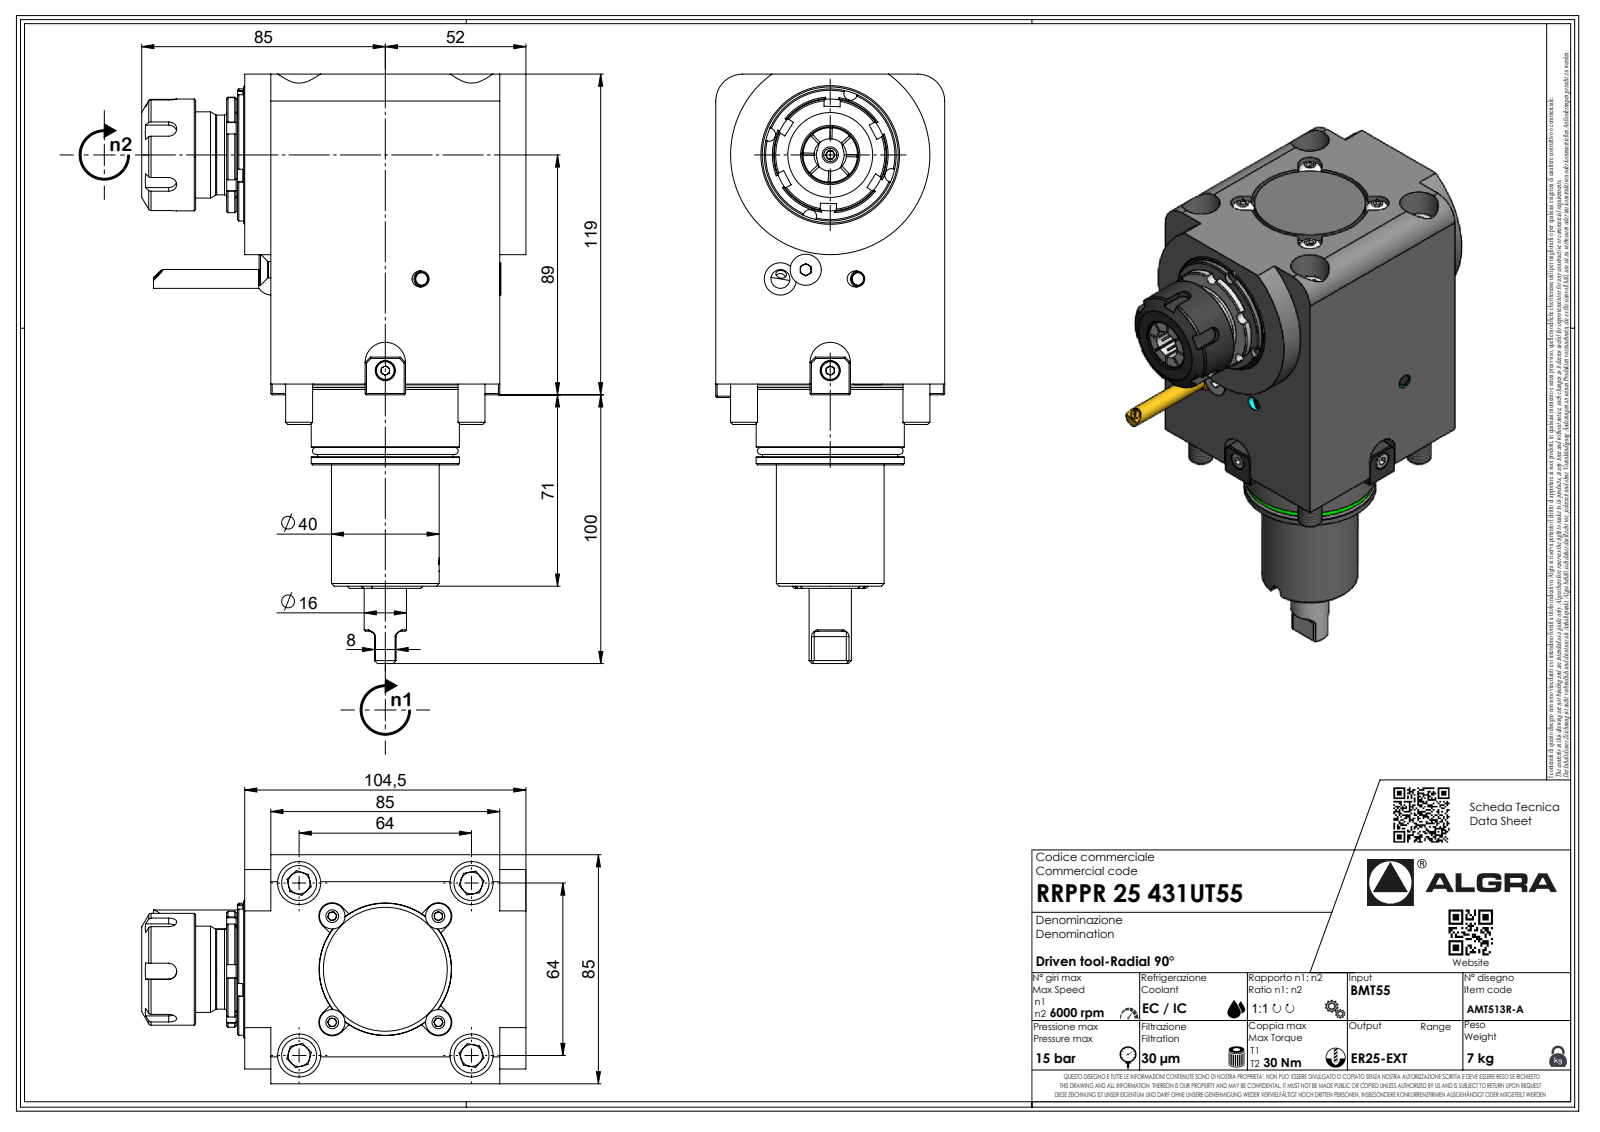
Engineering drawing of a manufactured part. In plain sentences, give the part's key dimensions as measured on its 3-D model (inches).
The part is named "RRPPR25431UT55". Its 3-D file was written by "SolidWorks 2016 (AUTOMOTIVE_DESIGN)". It is 1 solid with 591 faces: 376 planar, 78 cylindrical and 137 other. Overall it measures 8.61 by 5.444 by 3.346 inches. Its volume is 66.21 cubic inches and its surface area 125.1 square inches. Round holes: 1 of diameter 0.124, 1 of diameter 0.157. Round bosses or shafts: 4 of diameter 0.394, 1 of diameter 2.913, 1 of diameter 2.165, 1 of diameter 2.15, 1 of diameter 1.976, 1 of diameter 1.929, 1 of diameter 1.634, 1 of diameter 1.575. Partial cylindrical surfaces (rounded edges, fillets, slot ends): 10 of radius 0.098, 7 of radius 0.02, 7 of radius 0.031, 7 of radius 0.079, 7 of radius 0.219, 6 of radius 0.118, 2 of radius 0.394, 1 of radius 0.012. The main face-to-face distances are 3.346, 0.382, 3.728, 4.528, 4.11, 4.217, 3.835, 0.488, 0.106, 1.181.
